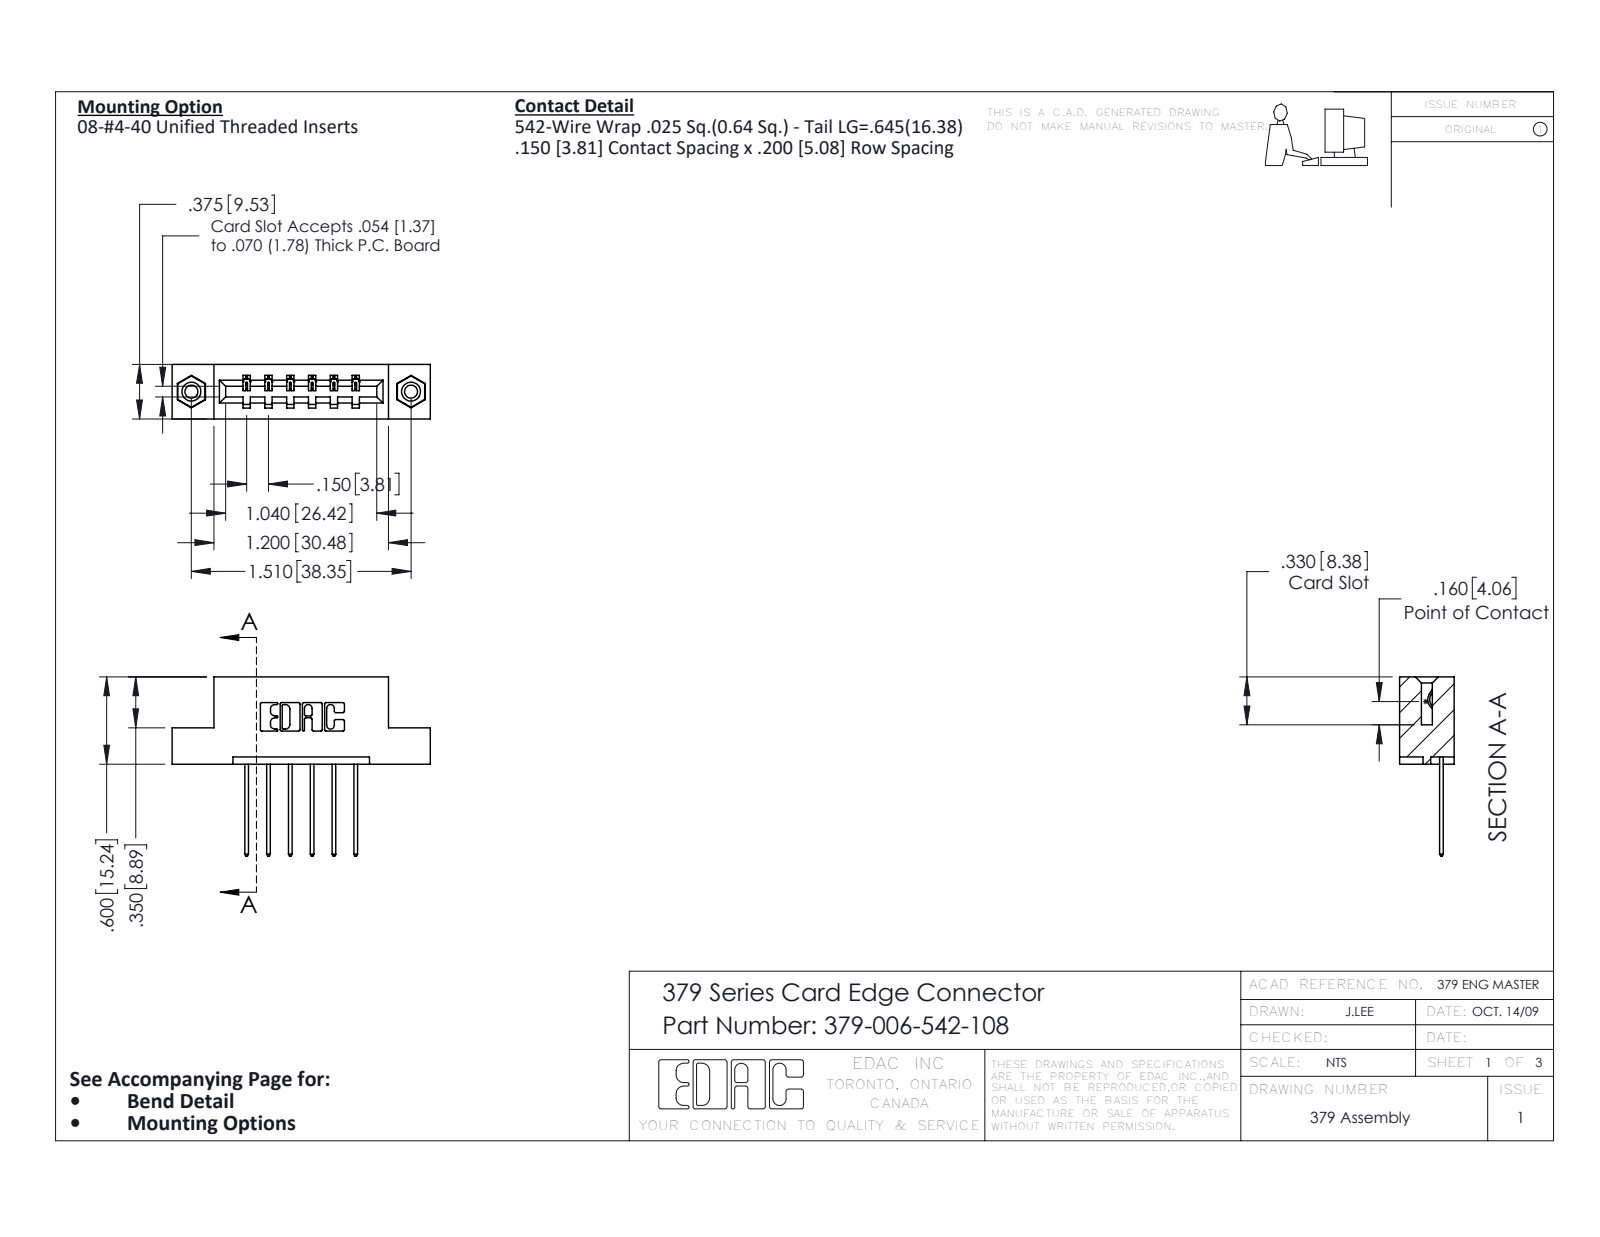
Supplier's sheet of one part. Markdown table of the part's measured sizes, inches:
| quantity | value |
| --- | --- |
| part name | 379 Part_Flush - .156 Dia - TI; 379-006-542-108; 345-250-001_345-250-003-102; 345-292-001_345-293-142 |
| STEP written by | SolidWorks 2016 (CONFIG_CONTROL_DESIGN) |
| units | inches |
| bodies | 9 solids, 522 faces (354 planar, 152 cylindrical, 16 other) |
| overall size | 1.775 × 1.232 × 0.375 |
| volume | 0.263 in³ |
| surface area | 6.747 in² |
| round holes (diameter × count) | 0.089 × 2, 0.125 × 2, 0.156 × 2 |
| round bosses / shafts (diameter × count) | 0.155 × 2 |
| partial cylindrical surfaces (radius × count) | 0.01 × 22, 0.006 × 12, 0.01 × 12, 0.007 × 6, 0.031 × 6, 0.026 × 3, 0.014 × 1, 0.022 × 1 |
| main face-to-face distances | 0.3, 0.2, 0.375, 0.05, 0.15, 0.075, 0.1, 0.25, 0.35, 0.6 |
| hole center spacings | 1.51 |
